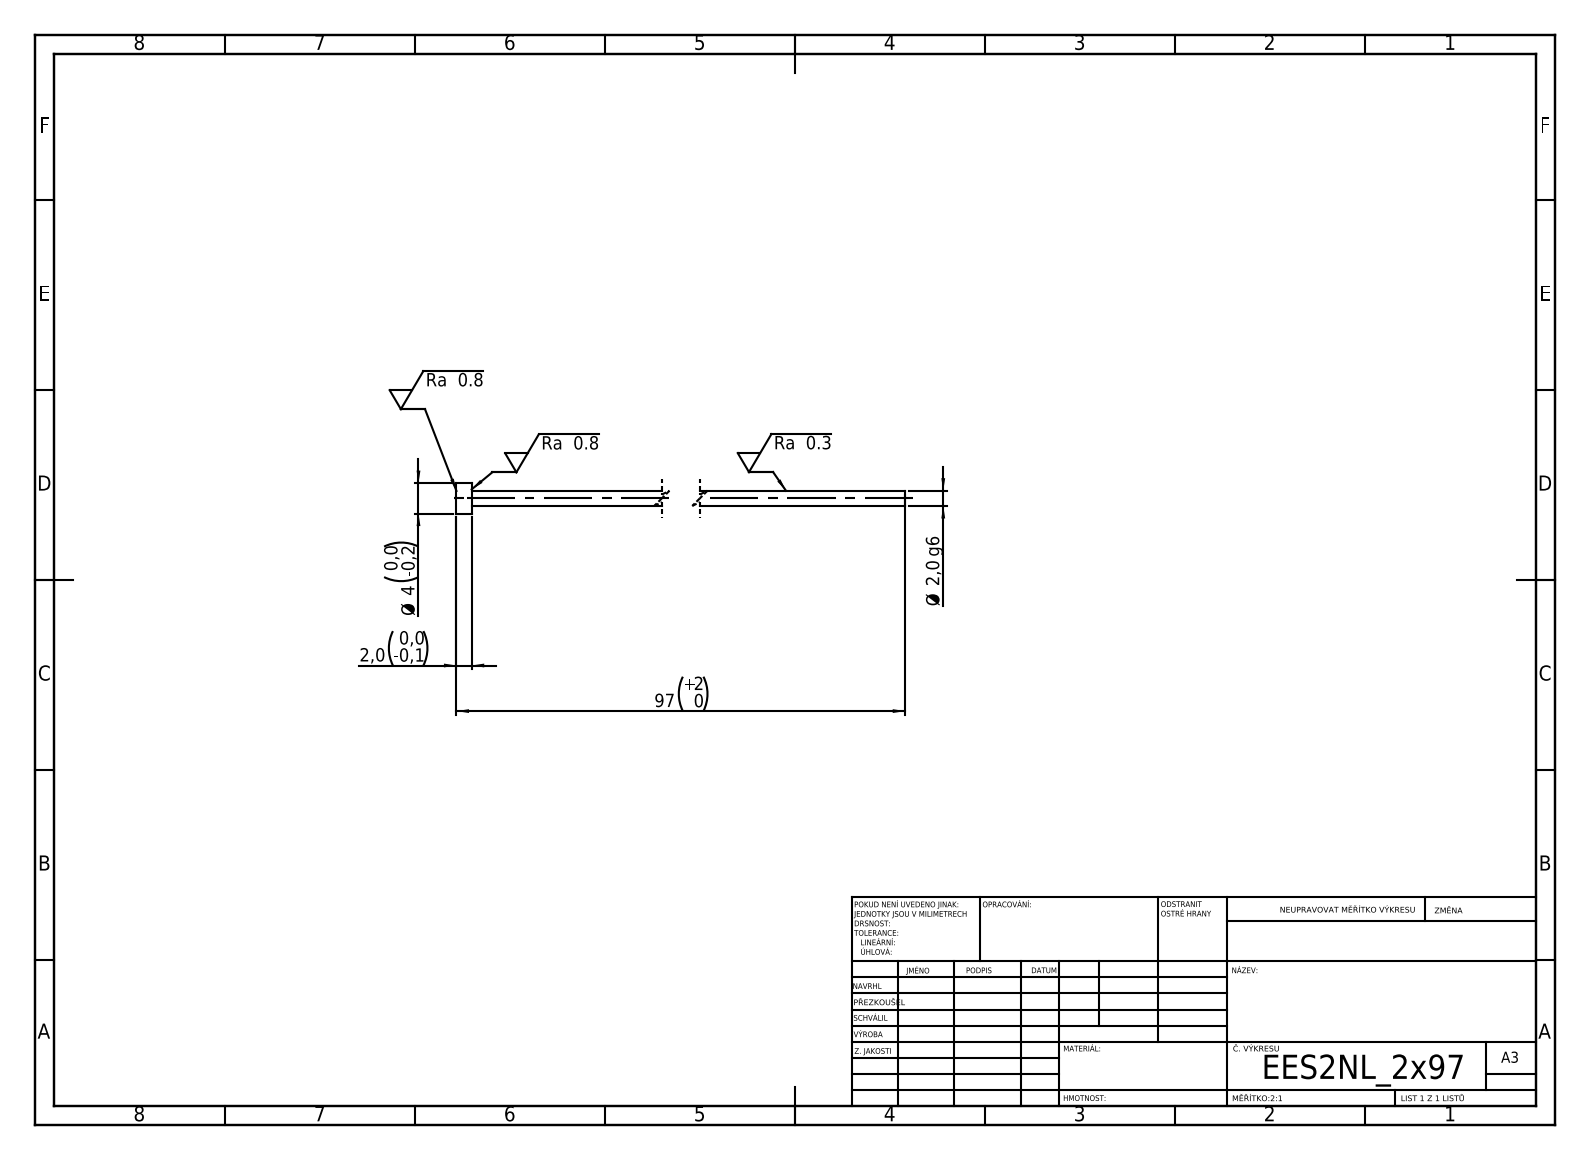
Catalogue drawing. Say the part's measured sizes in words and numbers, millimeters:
Its 3-D file was written by "SolidWorks 2019 (CONFIG_CONTROL_DESIGN)". It is 1 solid with 7 faces: 3 planar, 4 cylindrical and 0 other. Overall it measures 97 by 4 by 4 millimeters. Its volume is 324 cubic millimeters and its surface area 647 square millimeters. Round bosses or shafts: 1 of diameter 4, 1 of diameter 2. The main face-to-face distances are 2, 97, 95.
